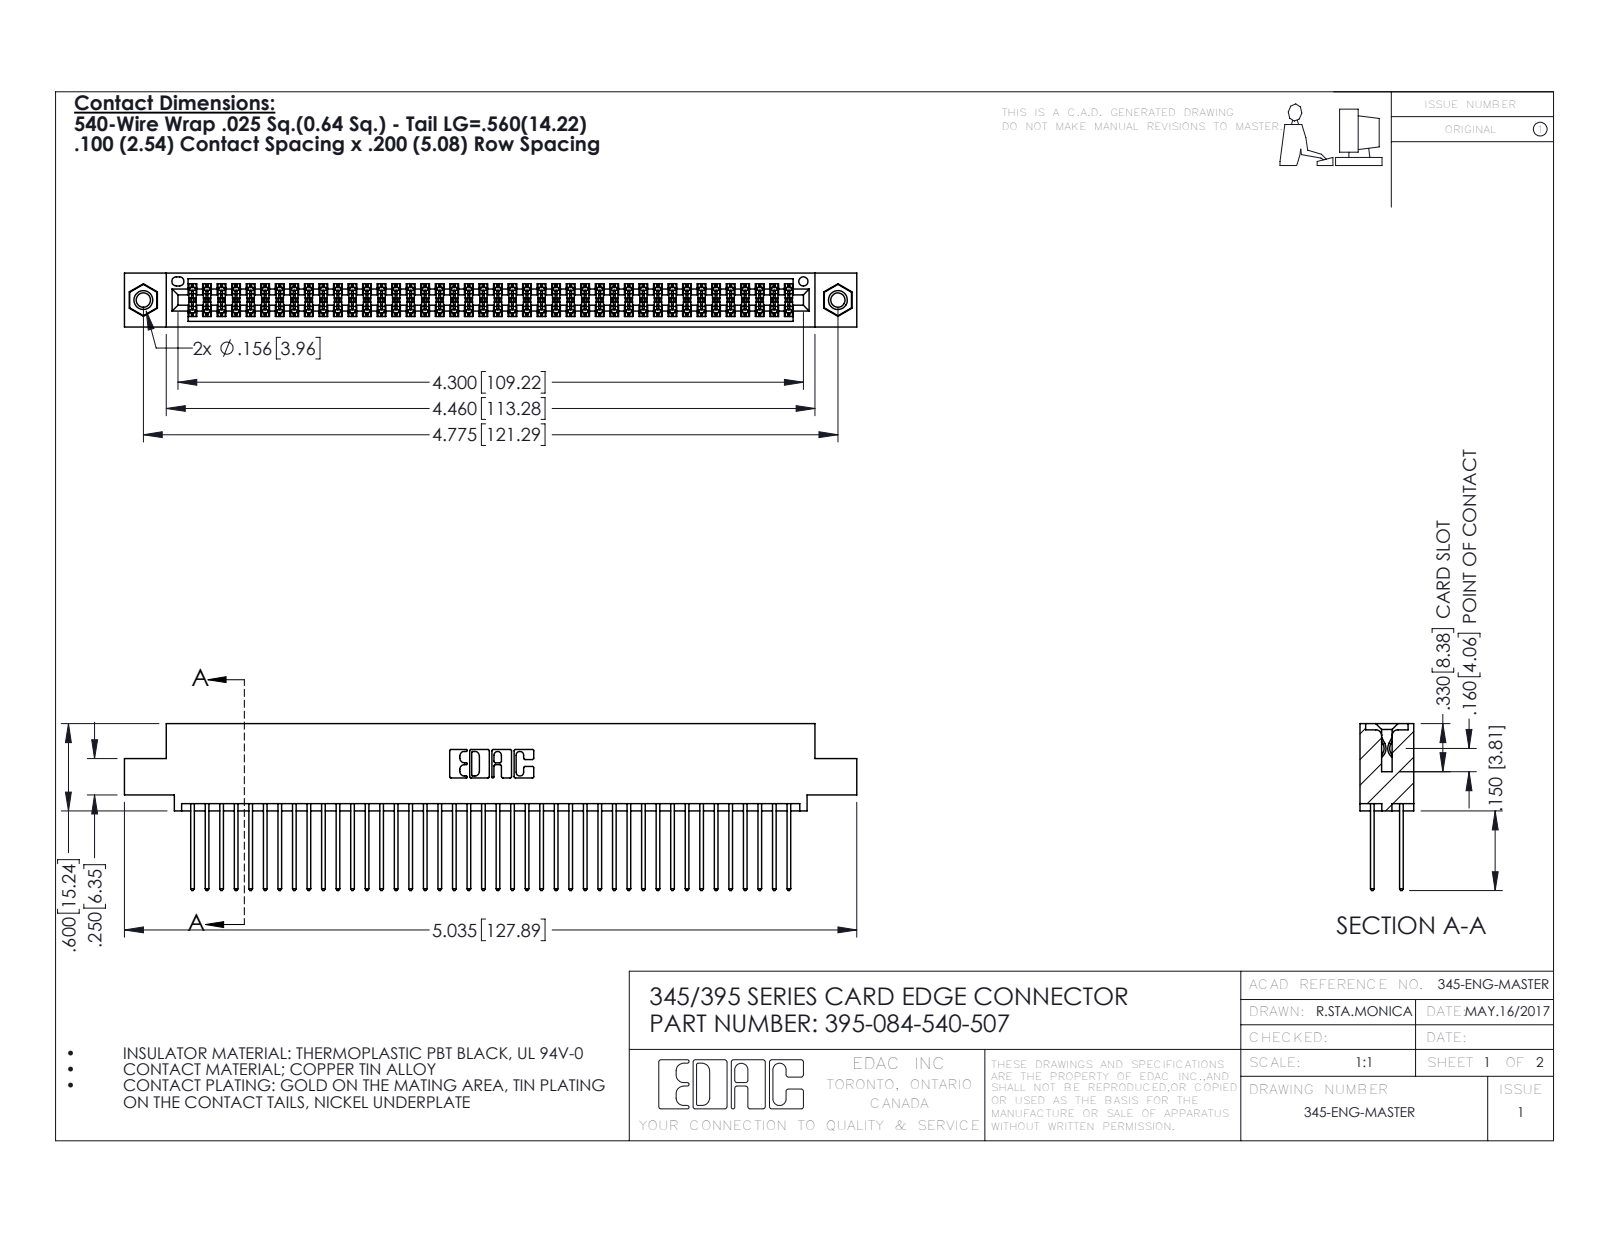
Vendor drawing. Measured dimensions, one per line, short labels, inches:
name: 345-292-001_345-293-140; 395-084-540-507; 345-250-001_345-250-005-103; 345 Part_0.110 Offset - 0.156 Dia-TI
written by: SolidWorks 2016 (CONFIG_CONTROL_DESIGN)
unit: in
bodies: 87 solids, 4390 faces (2888 planar, 1486 cylindrical, 16 other)
size: 5.035 × 1.147 × 0.37
volume: 0.772 in³; area: 31.47 in²
holes: 2× ⌀0.098, 2× ⌀0.125, 2× ⌀0.156, 1× ⌀0.064
bosses: 2× ⌀0.155
rounds: 126× R0.006, 84× R0.01, 22× R0.01, 6× R0.007, 6× R0.031, 3× R0.026, 2× R0.014, 2× R0.019
face distances: 0.072, 0.298, 0.2, 0.098, 0.272, 0.025, 0.37, 0.225, 0.175, 0.149
hole spacings: 0.27, 4.539, 4.775
